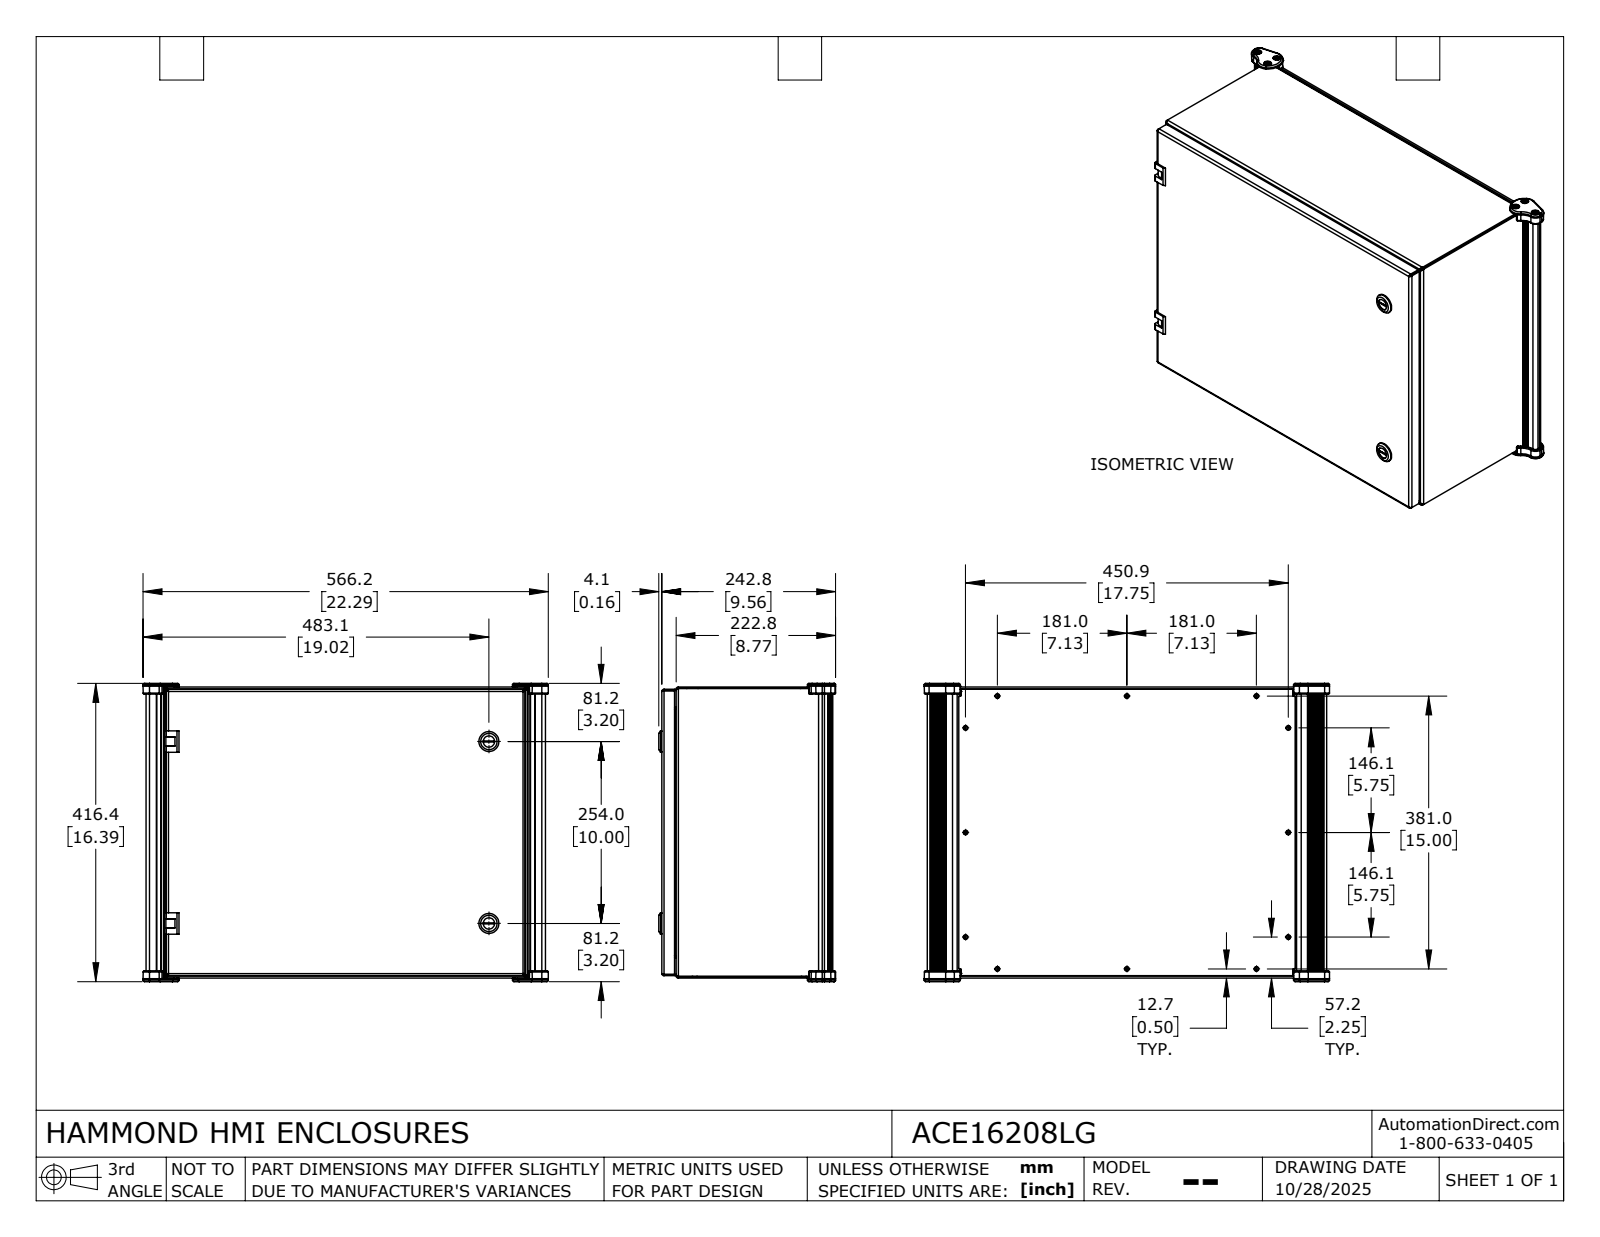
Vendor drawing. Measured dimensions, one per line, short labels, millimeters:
name: ACE16208LG
written by: SolidWorks 2024 (AUTOMOTIVE_DESIGN)
unit: mm
bodies: 99 solids, 2540 faces (1210 planar, 865 cylindrical, 465 other)
size: 566.22 × 416.43 × 246.86
volume: 2 756 000 mm³; area: 2 406 000 mm²
holes: 14× ⌀3.97, 14× ⌀5.94, 12× ⌀4.83, 6× ⌀5.2, 6× ⌀10.5, 5× ⌀4.98, 4× ⌀4.04, 4× ⌀10.32, 2× ⌀4.06, 2× ⌀5, 2× ⌀5.89, 2× ⌀6.35
bosses: 12× ⌀6.5, 6× ⌀6.35, 6× ⌀4.83, 6× ⌀3.79, 5× ⌀5.99, 4× ⌀9.53, 4× ⌀8.38, 2× ⌀27.94
rounds: 38× R0.25, 30× R1.5, 20× R1.03, 20× R3.09, 16× R0.4, 16× R0.75, 16× R1.27, 14× R1
face distances: 2.06, 224.3, 3.18, 404.34, 226.36, 3.17, 227.48, 229.54, 5.23, 505.94
hole spacings: 152.4, 254, 62.86, 128.24, 146.05, 180.97, 195.62, 229.76
